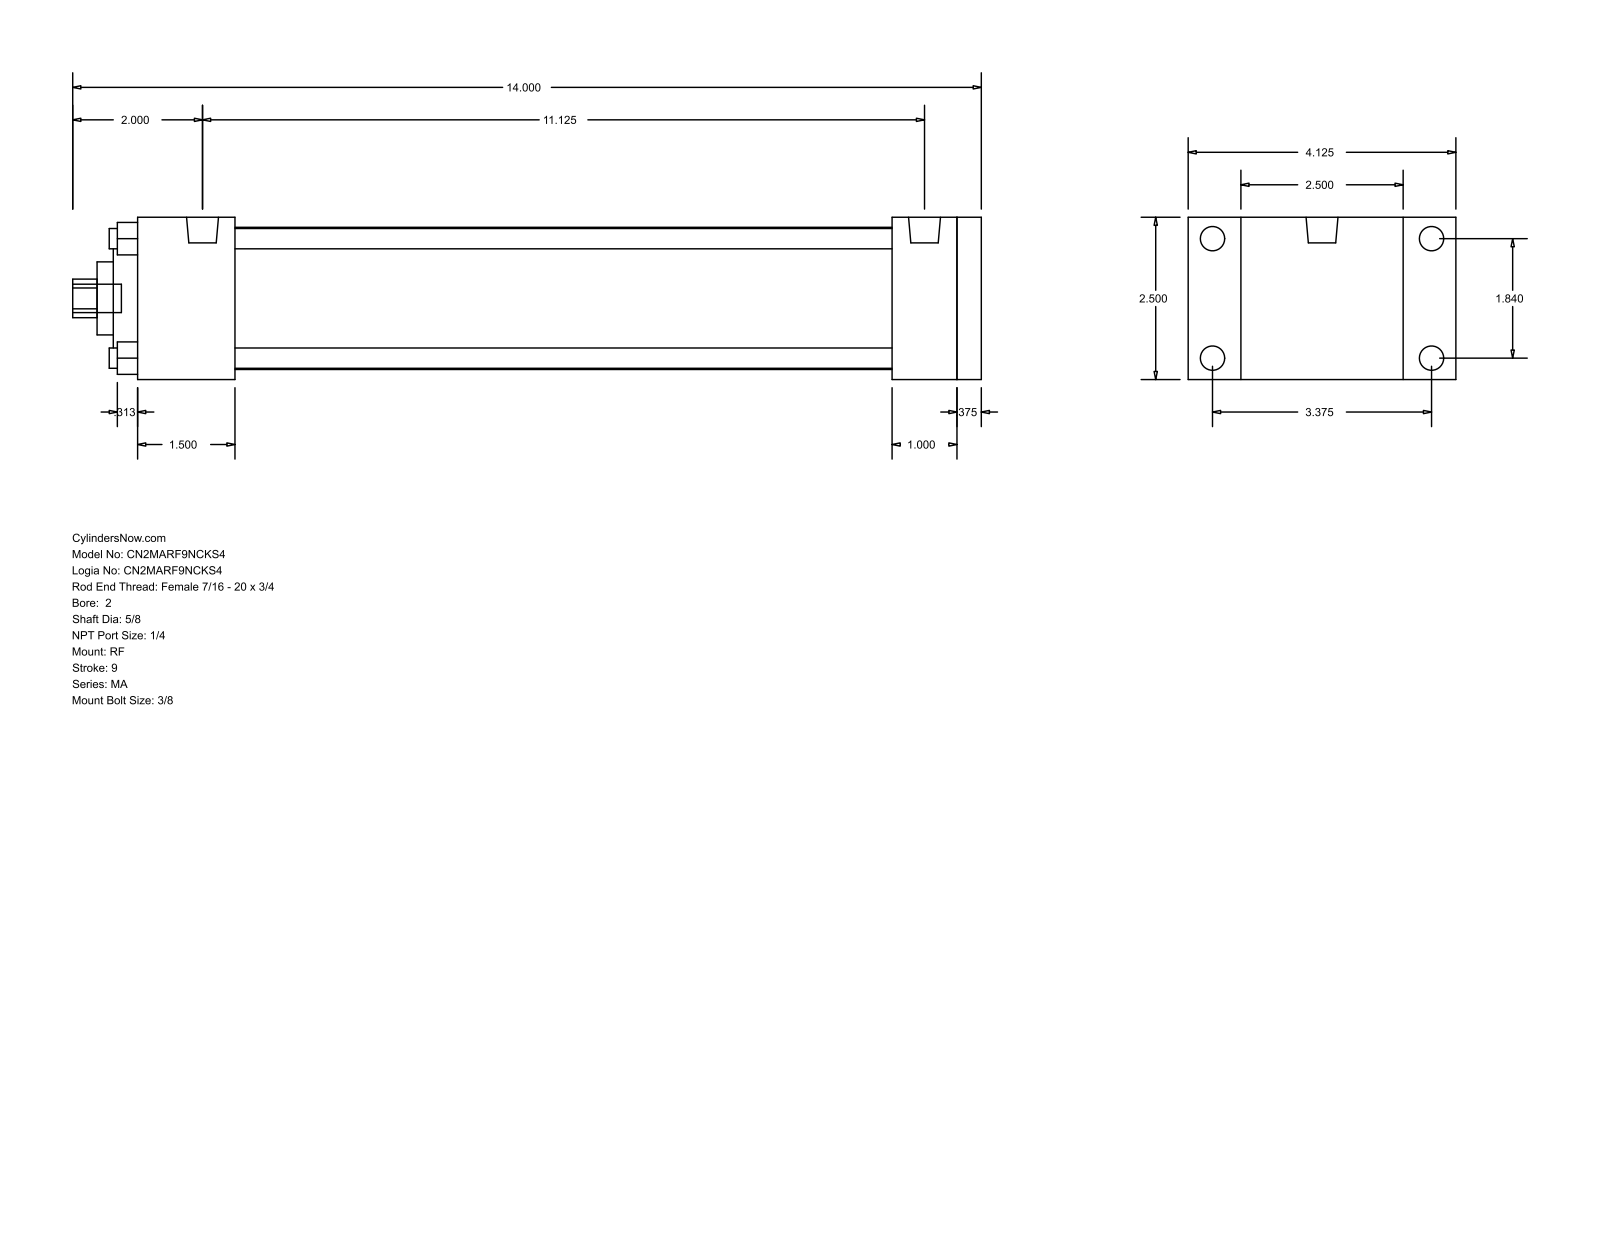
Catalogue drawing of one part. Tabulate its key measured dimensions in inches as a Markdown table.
| quantity | value |
| --- | --- |
| part name | MA_RF__0200_0.625 |
| STEP written by | GSSL Pune (CONFIG_CONTROL_DESIGN) |
| units | inches |
| bodies | 0 solids, 94 faces (65 planar, 29 cylindrical, 0 other) |
| overall size | 14 × 4.125 × 2.5 |
| round holes (diameter × count) | 0.313 × 4, 0.625 × 1, 1.125 × 1, 2 × 1, 2.19 × 1 |
| round bosses / shafts (diameter × count) | 0.375 × 4, 0.313 × 4, 0.492 × 2, 0.437 × 1 |
| partial cylindrical surfaces (radius × count) | 0.297 × 1 |
| main face-to-face distances | 2.5, 0.375, 1.5, 0.375, 12.625, 13, 13.375, 11.125, 11.5, 11.625 |
| hole center spacings | 1.301, 1.84, 2.602 |
